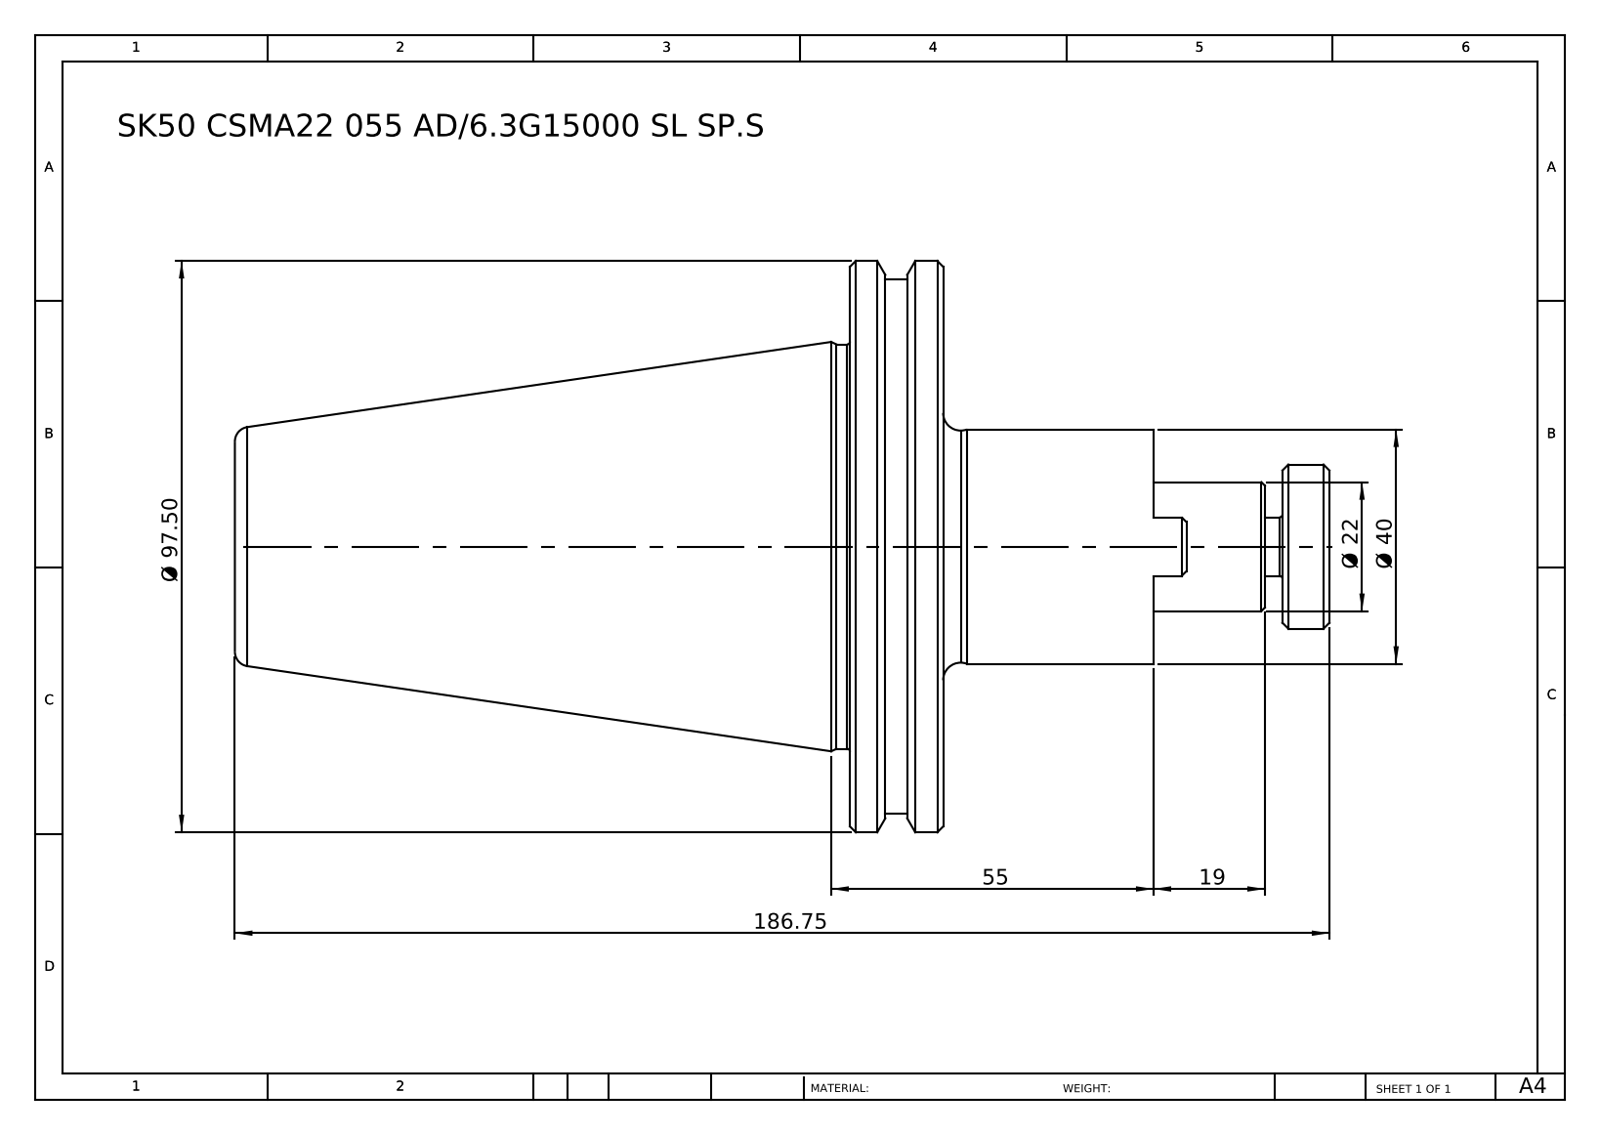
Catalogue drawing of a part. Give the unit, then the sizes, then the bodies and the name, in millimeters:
Units: millimetres
Overall size (bounding box): 186.75 × 97.5 × 97.5
Round bosses / shafts (diameter × count): ⌀97.5 ×1, ⌀91.27 ×1, ⌀69 ×1, ⌀40 ×1, ⌀28 ×1, ⌀22 ×1, ⌀10 ×1
Partial cylindrical surfaces — rounded edges, fillets, slot ends (radius × count): R13 ×1
Main face-to-face distances: 15.9, 120.85, 104.95, 35.9, 51.8, 156.75, 30, 65.9, 81.8, 186.75
Volume: 431 892 mm³ · Surface area: 44 251 mm²
Bodies: 1 solid, 70 faces (20 planar, 18 cylindrical, 32 other)
Part name (STEP PRODUCT): SK 50 CSMA22 055 AD-6.3G15000 SL SP
STEP written by: SolidWorks 2014 (CONFIG_CONTROL_DESIGN)
